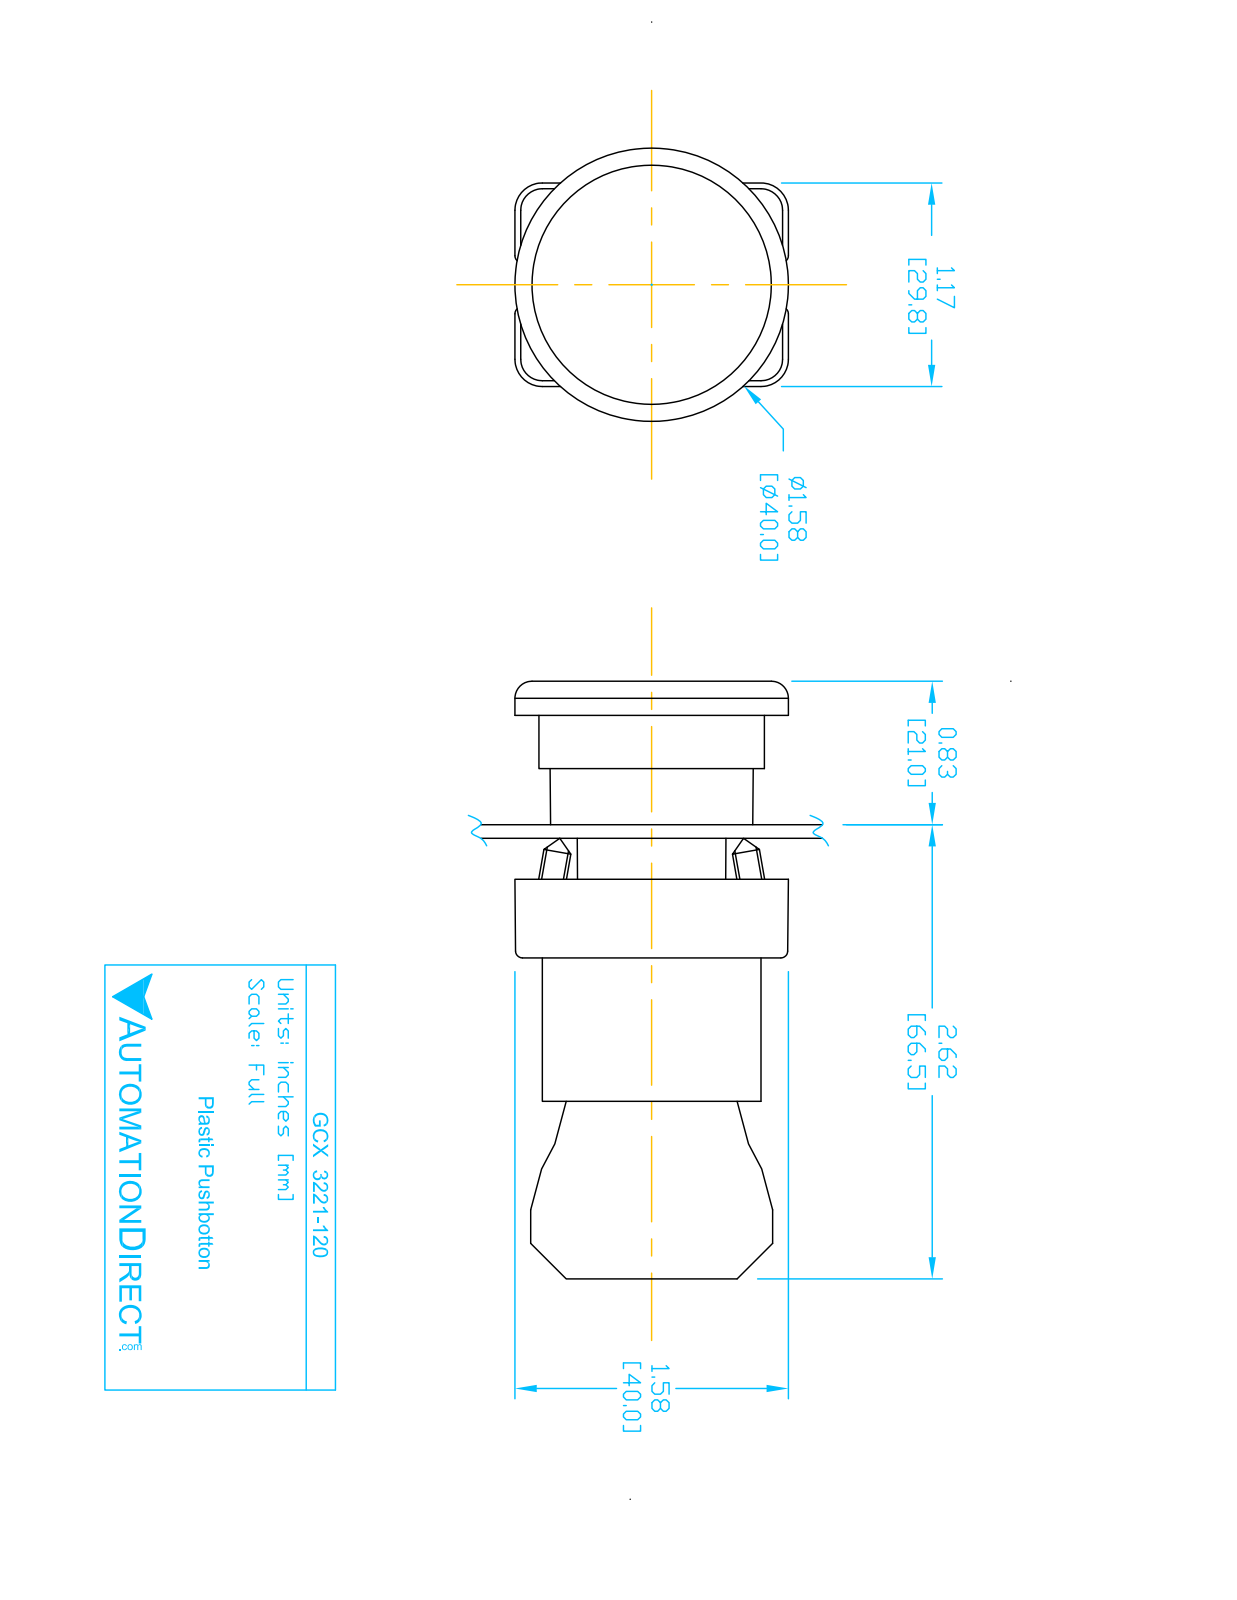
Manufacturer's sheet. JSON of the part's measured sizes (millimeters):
{"part_name": "GCX322X OPERATOR; ECX3029-2; ECX1050; GCX3221-120 (+1 more)", "step_written_by": "SolidWorks 2016 (AUTOMOTIVE_DESIGN)", "units": "millimeters", "bodies": {"solids": 7, "faces": 431, "planar": 252, "cylindrical": 146, "other": 33}, "overall_size": [88.1, 40.2, 40], "volume_mm3": 47440, "surface_area_mm2": 26380, "round_holes": [[2, 2], [3.1, 2], [3.3, 2], [2.2, 1], [5, 1], [11.9, 1], [22.3, 1], [22.6, 1], [26, 1], [30, 1]], "round_bosses_or_shafts": [[4, 4], [33, 1], [29.8, 1], [24, 1], [21.7, 1], [19.8, 1], [12.8, 1]], "partial_cylinders_radius": [[1.5, 24], [1, 12], [3.1, 12], [4, 12], [1, 8], [3.3, 2], [0.5, 1], [1.6, 1]], "face_to_face_distances": [21, 62.1, 41.1, 14.7, 58.1, 37.1, 4, 14.9, 0.8, 29.6], "hole_center_spacings": [6, 13.7, 12, 12.3]}
